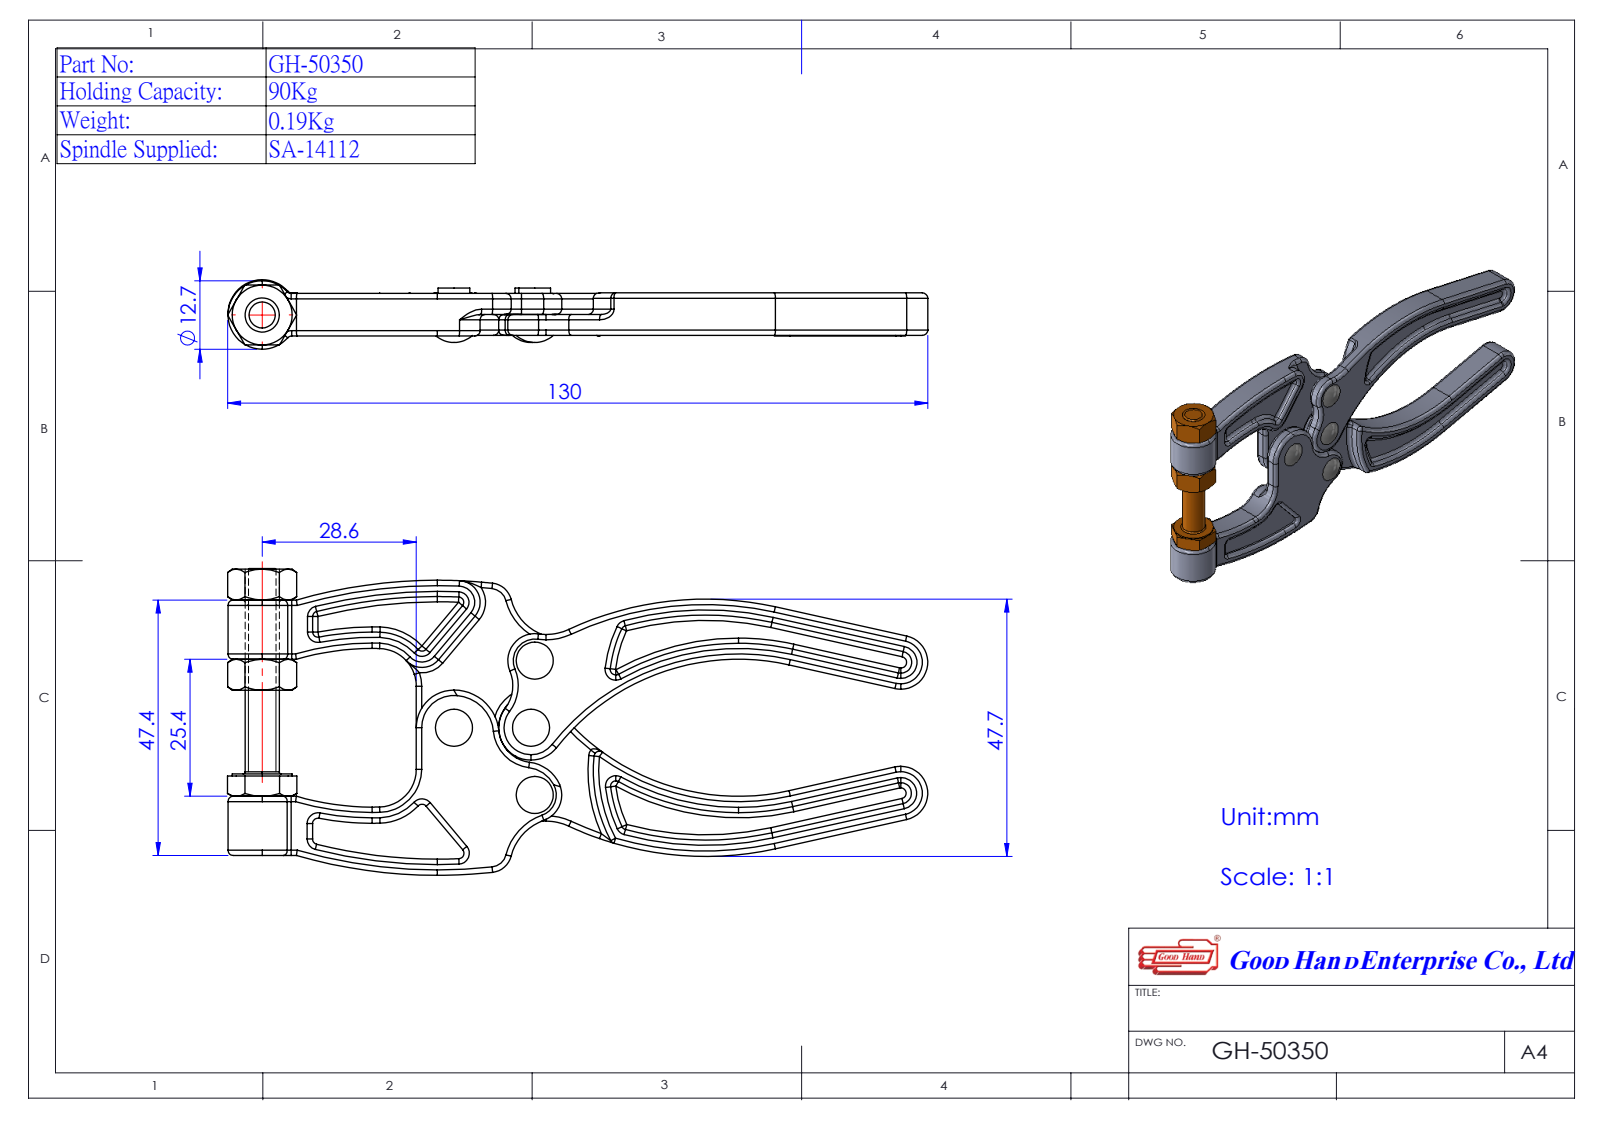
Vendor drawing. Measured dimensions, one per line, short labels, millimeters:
name: Group2^493799(GH-50350); 493799(GH-50350); 35035001-1^493799(GH-50350); Group1^493799(GH-50350) (+1 more)
written by: SolidWorks 2016 (AUTOMOTIVE_DESIGN)
unit: mm
bodies: 4 solids, 246 faces (90 planar, 144 cylindrical, 12 other)
size: 131.49 × 56.85 × 14.28
volume: 24 588 mm³; area: 16 420 mm²
holes: 4× ⌀3
bosses: 4× ⌀6, 1× ⌀15, 1× ⌀11.13, 1× ⌀6.35
rounds: 10× R1, 6× R4, 4× R5, 4× R7, 4× R10, 3× R6, 2× R2, 2× R5.5
face distances: 3.9, 2, 7.8, 4.4, 1.4, 1.9, 2.5, 3, 0.5, 5.8
hole spacings: 12.52, 18.92, 13.5, 25
